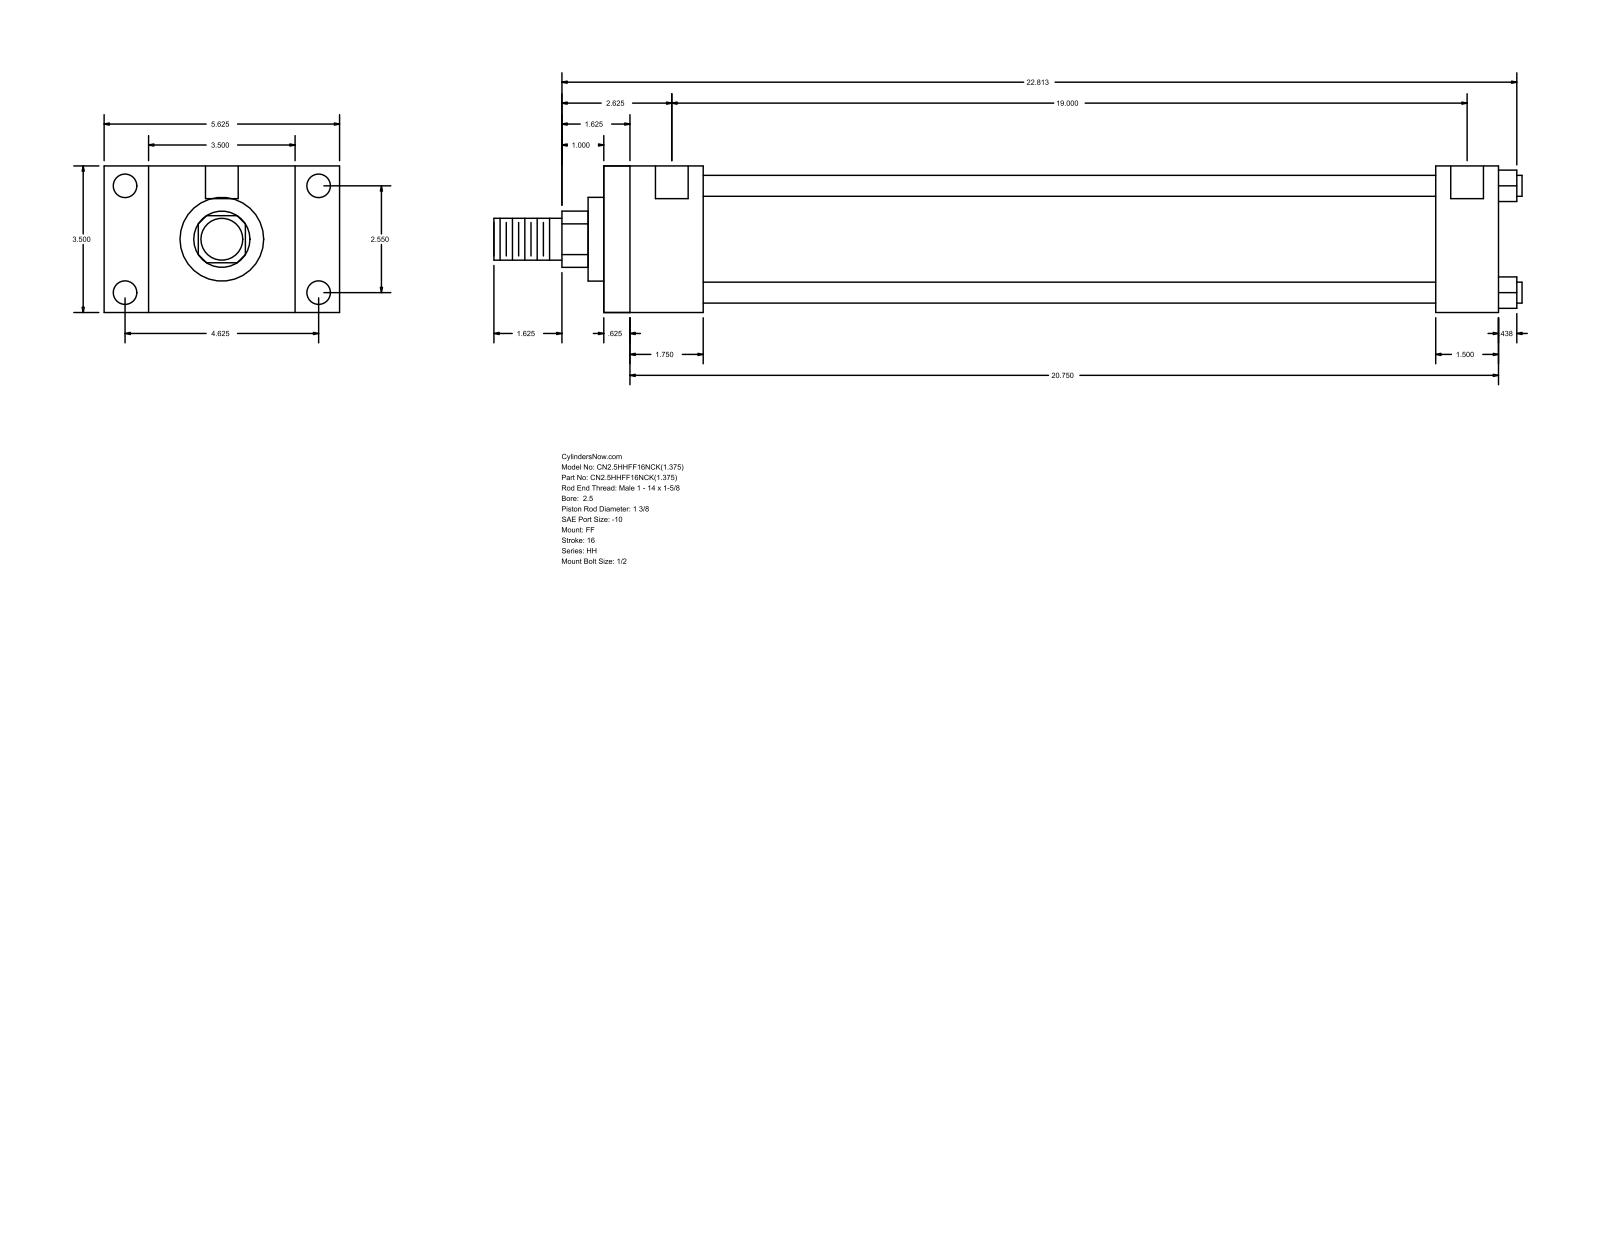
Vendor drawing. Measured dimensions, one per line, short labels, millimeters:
name: HH_FF__0250_1.375
written by: GSSL Pune (CONFIG_CONTROL_DESIGN)
unit: mm
bodies: 0 solids, 92 faces (64 planar, 28 cylindrical, 0 other)
size: 623.89 × 142.88 × 88.9
holes: 4× ⌀5.56, 4× ⌀14.3, 2× ⌀19.84
bosses: 4× ⌀12.7, 1× ⌀73.03, 1× ⌀50.8, 1× ⌀34.92, 1× ⌀25.4
rounds: 1× R17.06
face distances: 88.9, 542.93, 15.87, 527.06, 60.32, 44.45, 482.61, 504.83, 488.96, 444.51
hole spacings: 64.76, 117.48, 134.15, 485.77, 1.58, 1.59, 482.6, 484.18
